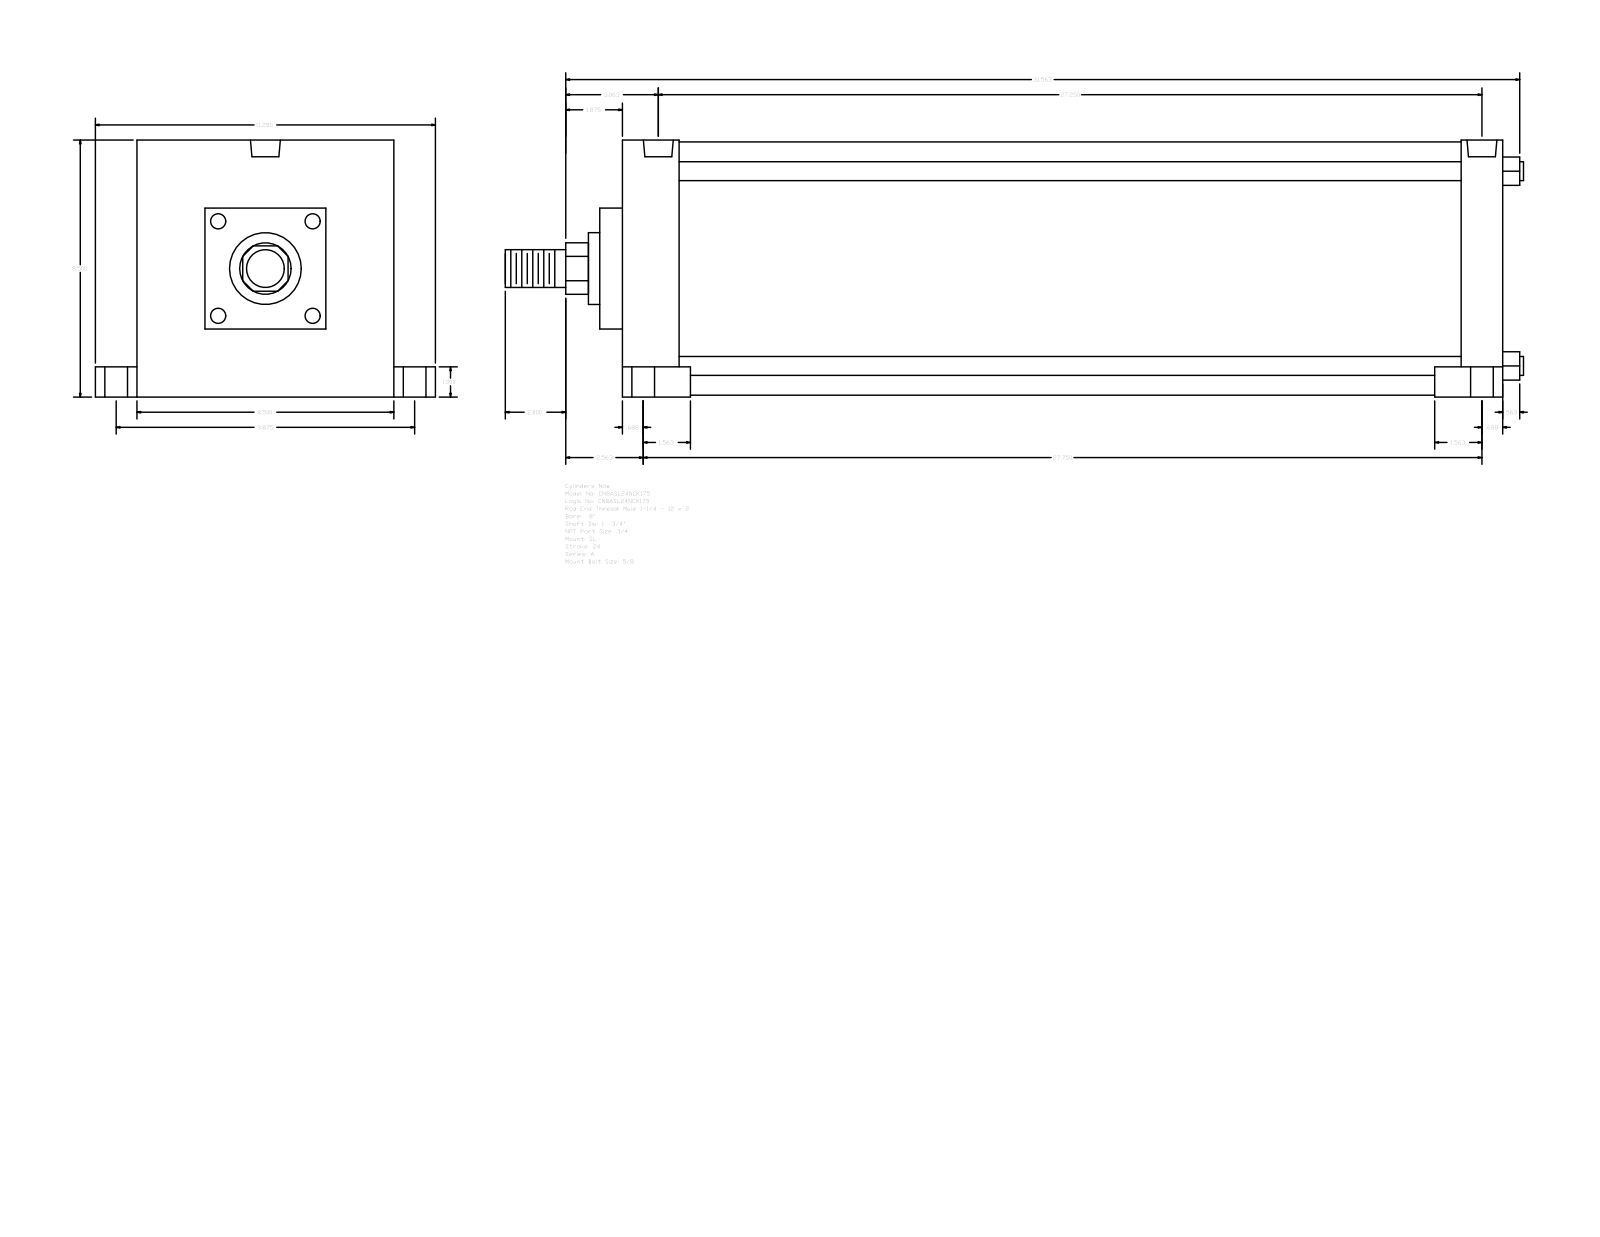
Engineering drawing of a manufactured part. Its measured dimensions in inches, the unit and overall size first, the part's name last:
Units: inches
Overall size (bounding box): 33.687 × 11.25 × 8.5
Round holes (diameter × count): ⌀0.594 ×4, ⌀0.75 ×4, ⌀1 ×4, ⌀0.989 ×2
Round bosses / shafts (diameter × count): ⌀0.625 ×4, ⌀8.375 ×1, ⌀2.375 ×1, ⌀1.75 ×1, ⌀1.25 ×1
Partial cylindrical surfaces — rounded edges, fillets, slot ends (radius × count): R0.852 ×1
Main face-to-face distances: 29.125, 8.5, 1.375, 1.875, 27.25, 27.75, 25.875, 2.25, 0.75, 6.25
Hole centre spacings: 0.25, 4.937, 4.944, 4.963, 4.994, 9.875, 26.75, 27
Bodies: 0 solids, 117 faces (85 planar, 32 cylindrical, 0 other)
Part name (STEP PRODUCT): A_SL__0800_1.75
STEP written by: GSSL Pune (CONFIG_CONTROL_DESIGN)
